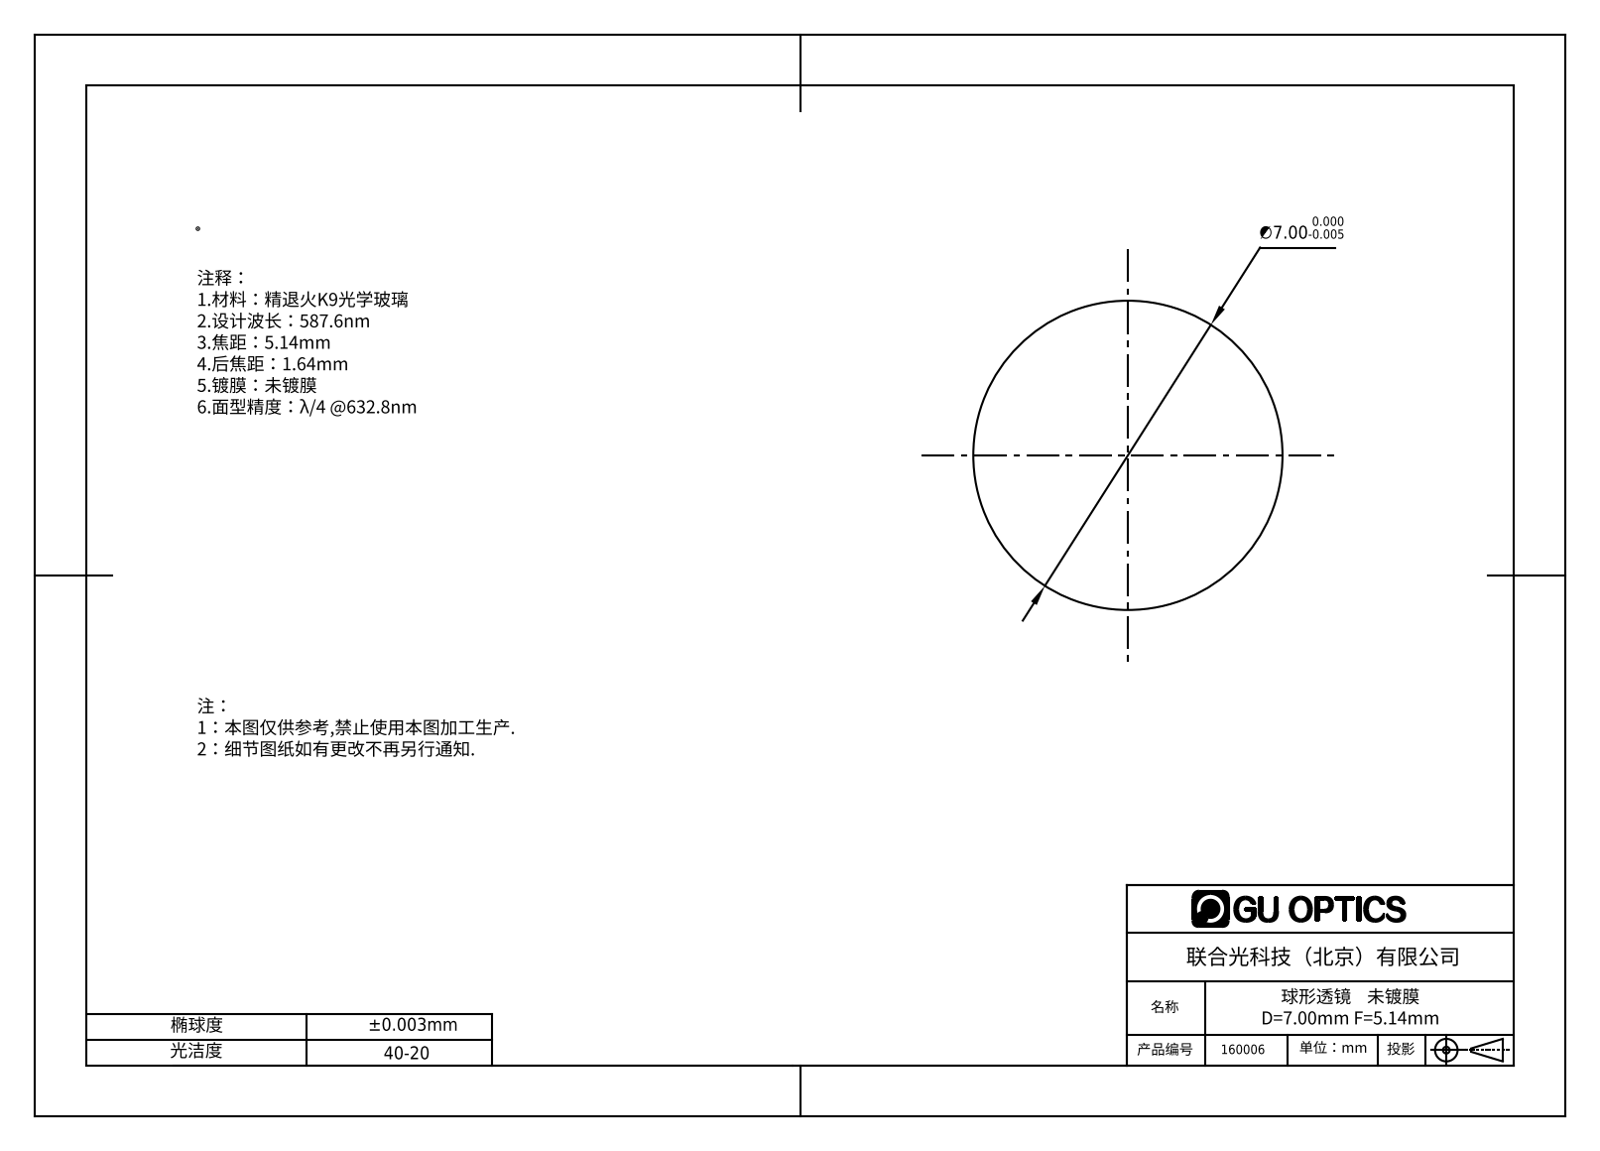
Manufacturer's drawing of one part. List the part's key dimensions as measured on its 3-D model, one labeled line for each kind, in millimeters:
Part name (STEP PRODUCT): 160006
STEP written by: SolidWorks 2016 (CONFIG_CONTROL_DESIGN)
Units: millimetres
Bodies: 1 solid, 2 faces (0 planar, 0 cylindrical, 2 other)
Overall size (bounding box): 7 × 7 × 7
Volume: 180 mm³ · Surface area: 154 mm²
